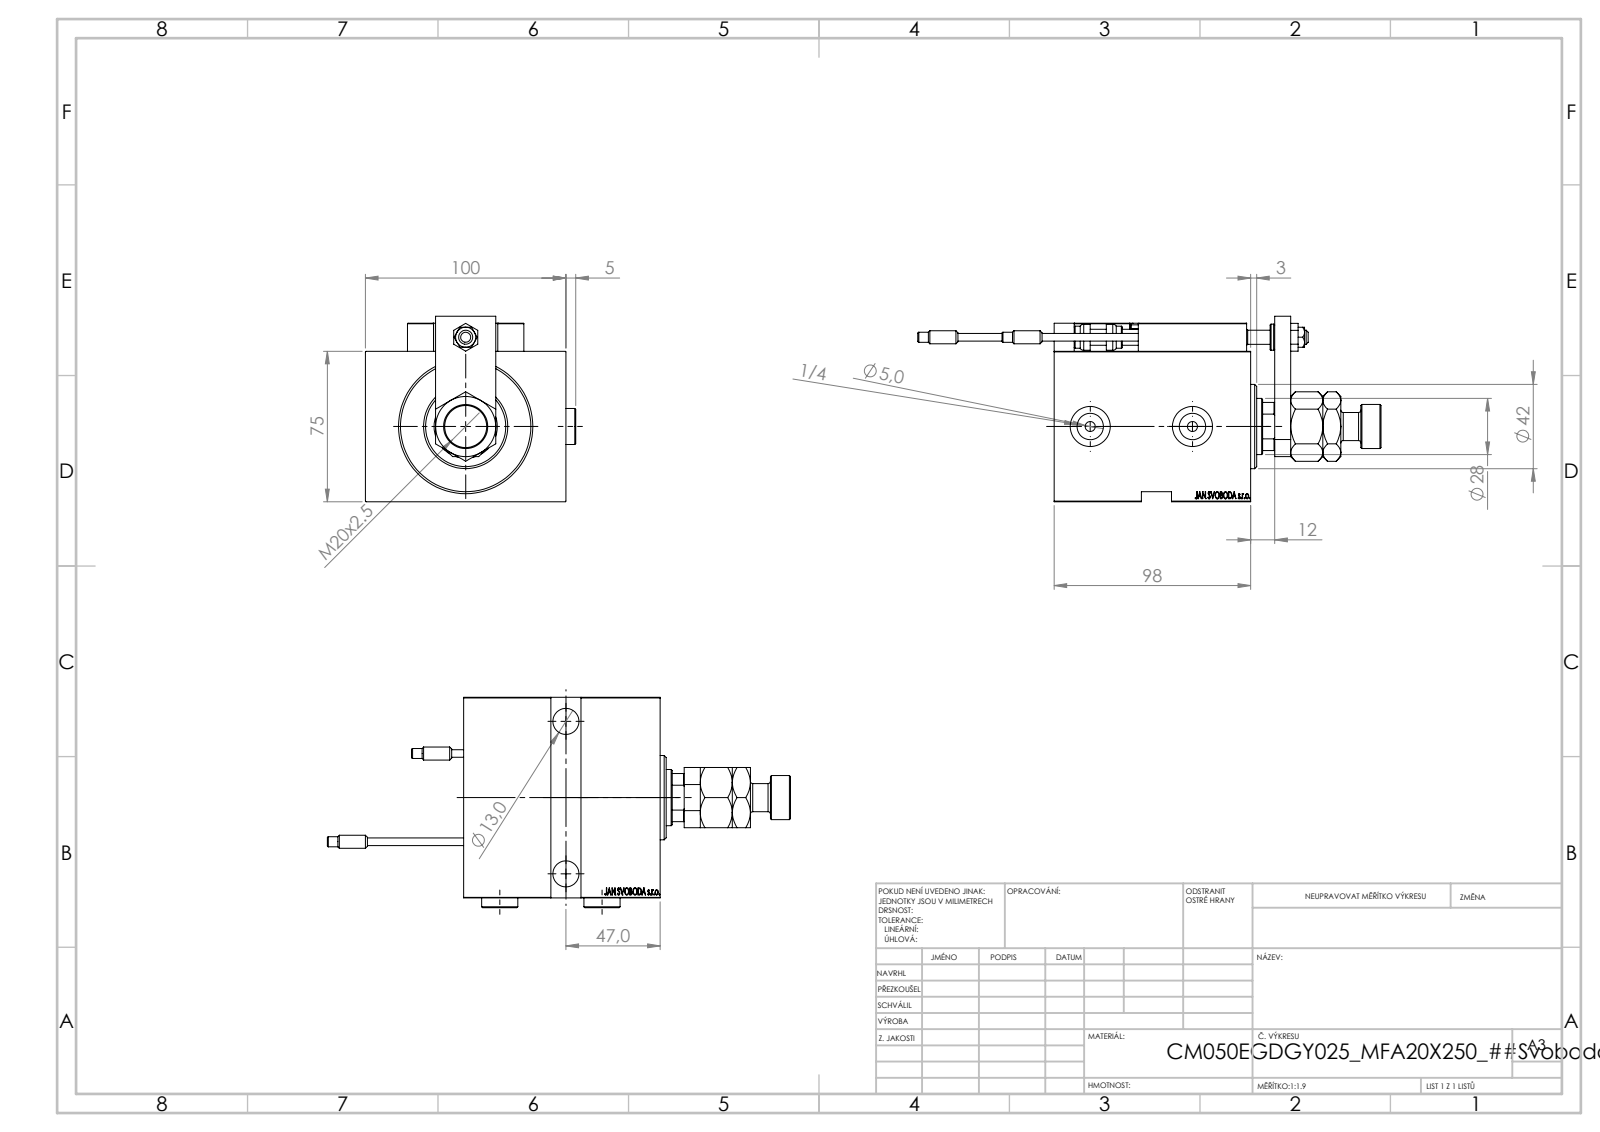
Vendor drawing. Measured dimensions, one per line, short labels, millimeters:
name: ALLEN BOLT D8; TYC_L79; V450CM_E_VCP; V450CM_E_Body (+7 more)
written by: SolidWorks 2019 (CONFIG_CONTROL_DESIGN)
unit: mm
bodies: 27 solids, 1413 faces (622 planar, 202 cylindrical, 589 other)
size: 231 × 104.9 × 92.5
volume: 753 870 mm³; area: 134 725 mm²
holes: 5× ⌀8, 4× ⌀3.2, 4× ⌀4, 4× ⌀5, 3× ⌀20, 2× ⌀13, 2× ⌀13.16, 2× ⌀19, 1× ⌀7, 1× ⌀18.5, 1× ⌀28, 1× ⌀31.5
bosses: 4× ⌀5, 2× ⌀18, 2× ⌀6.5, 2× ⌀3.8, 1× ⌀52, 1× ⌀42, 1× ⌀22, 1× ⌀14
rounds: 30× R0.3, 2× R3, 1× R13.5
face distances: 75, 14, 100, 98, 84, 5, 25, 79, 20, 32
hole spacings: 11.37, 20, 29.59, 29.69, 36.06, 42.19, 48.83, 50.04
